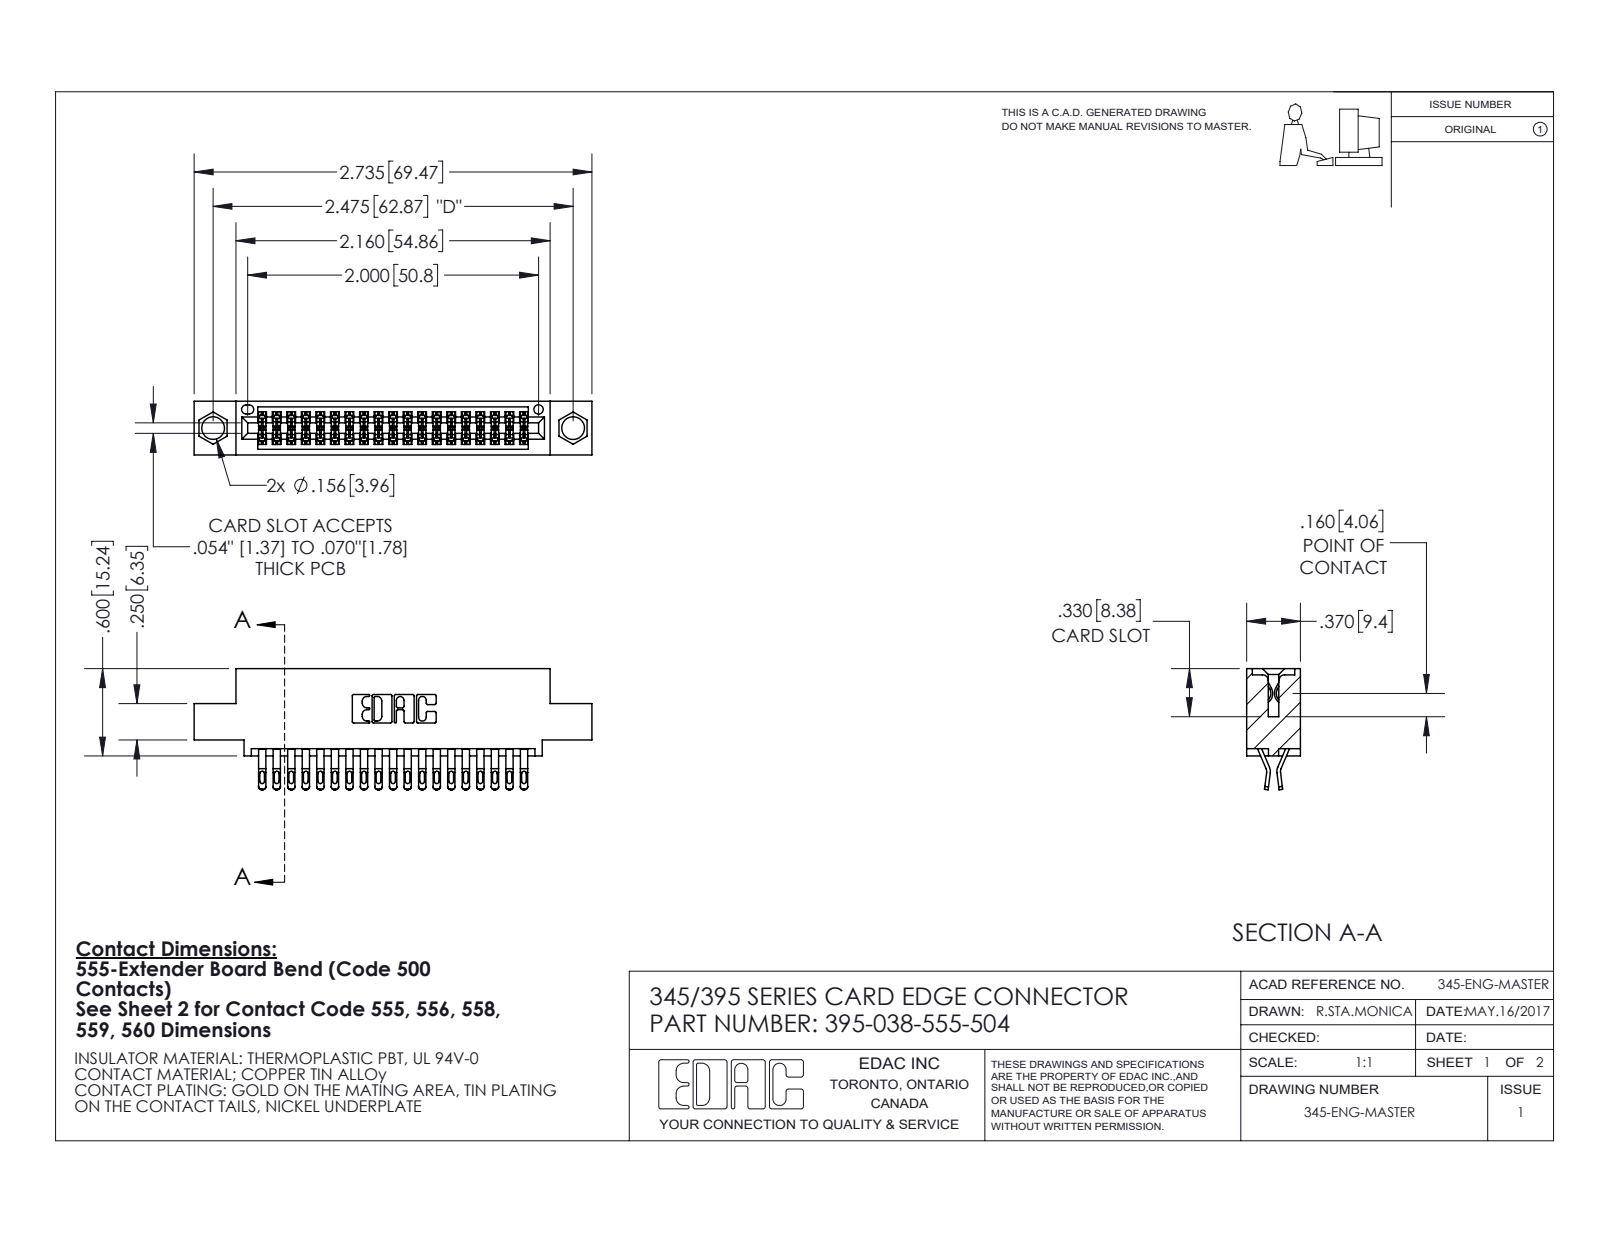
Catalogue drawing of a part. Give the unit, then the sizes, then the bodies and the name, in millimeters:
Units: millimetres
Overall size (bounding box): 69.5 × 21.1 × 9.4
Round holes (diameter × count): ⌀4 ×2, ⌀1.6 ×1
Partial cylindrical surfaces — rounded edges, fillets, slot ends (radius × count): R0.4 ×95, R0.2 ×76, R0.5 ×76, R0.3 ×22, R0.2 ×6, R0.8 ×6, R0.7 ×3, R0.3 ×2
Main face-to-face distances: 7.6, 1.8, 5.1, 9.4, 0.6, 2.5, 6.9, 5.7, 4.4, 3.8
Hole centre spacings: 6.9, 56.9, 62.9
Volume: 6 470 mm³ · Surface area: 9 439 mm²
Bodies: 39 solids, 2272 faces (1276 planar, 996 cylindrical, 0 other)
Part name (STEP PRODUCT): 345-292-001_555 Tail; 345 Part_0.110 Offset - 0.156 Dia-TI; 395-038-555-504
STEP written by: SolidWorks 2020 (CONFIG_CONTROL_DESIGN)
